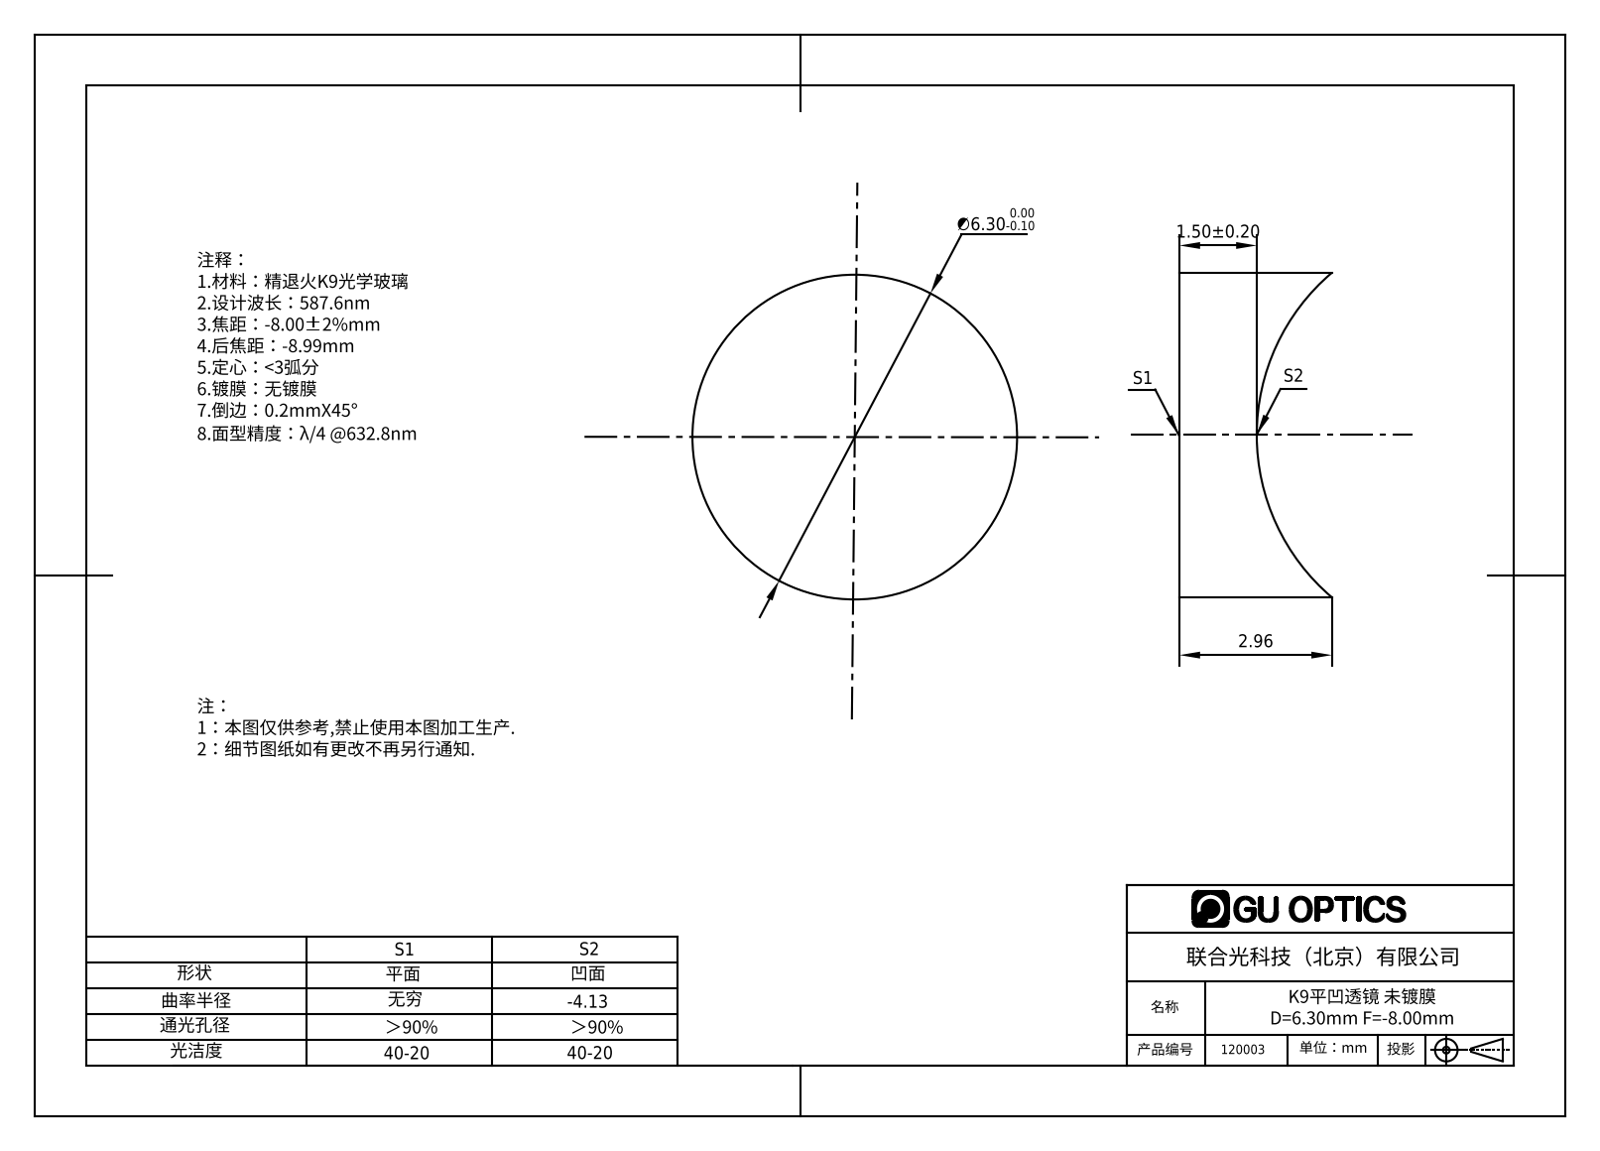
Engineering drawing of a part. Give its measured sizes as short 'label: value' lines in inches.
name: 120003
written by: SolidWorks 2016 (AUTOMOTIVE_DESIGN)
unit: in
bodies: 1 solid, 5 faces (1 planar, 2 cylindrical, 2 other)
size: 0.248 × 0.248 × 0.117
volume: 0.004 in³; area: 0.198 in²
bosses: 1× ⌀0.248
